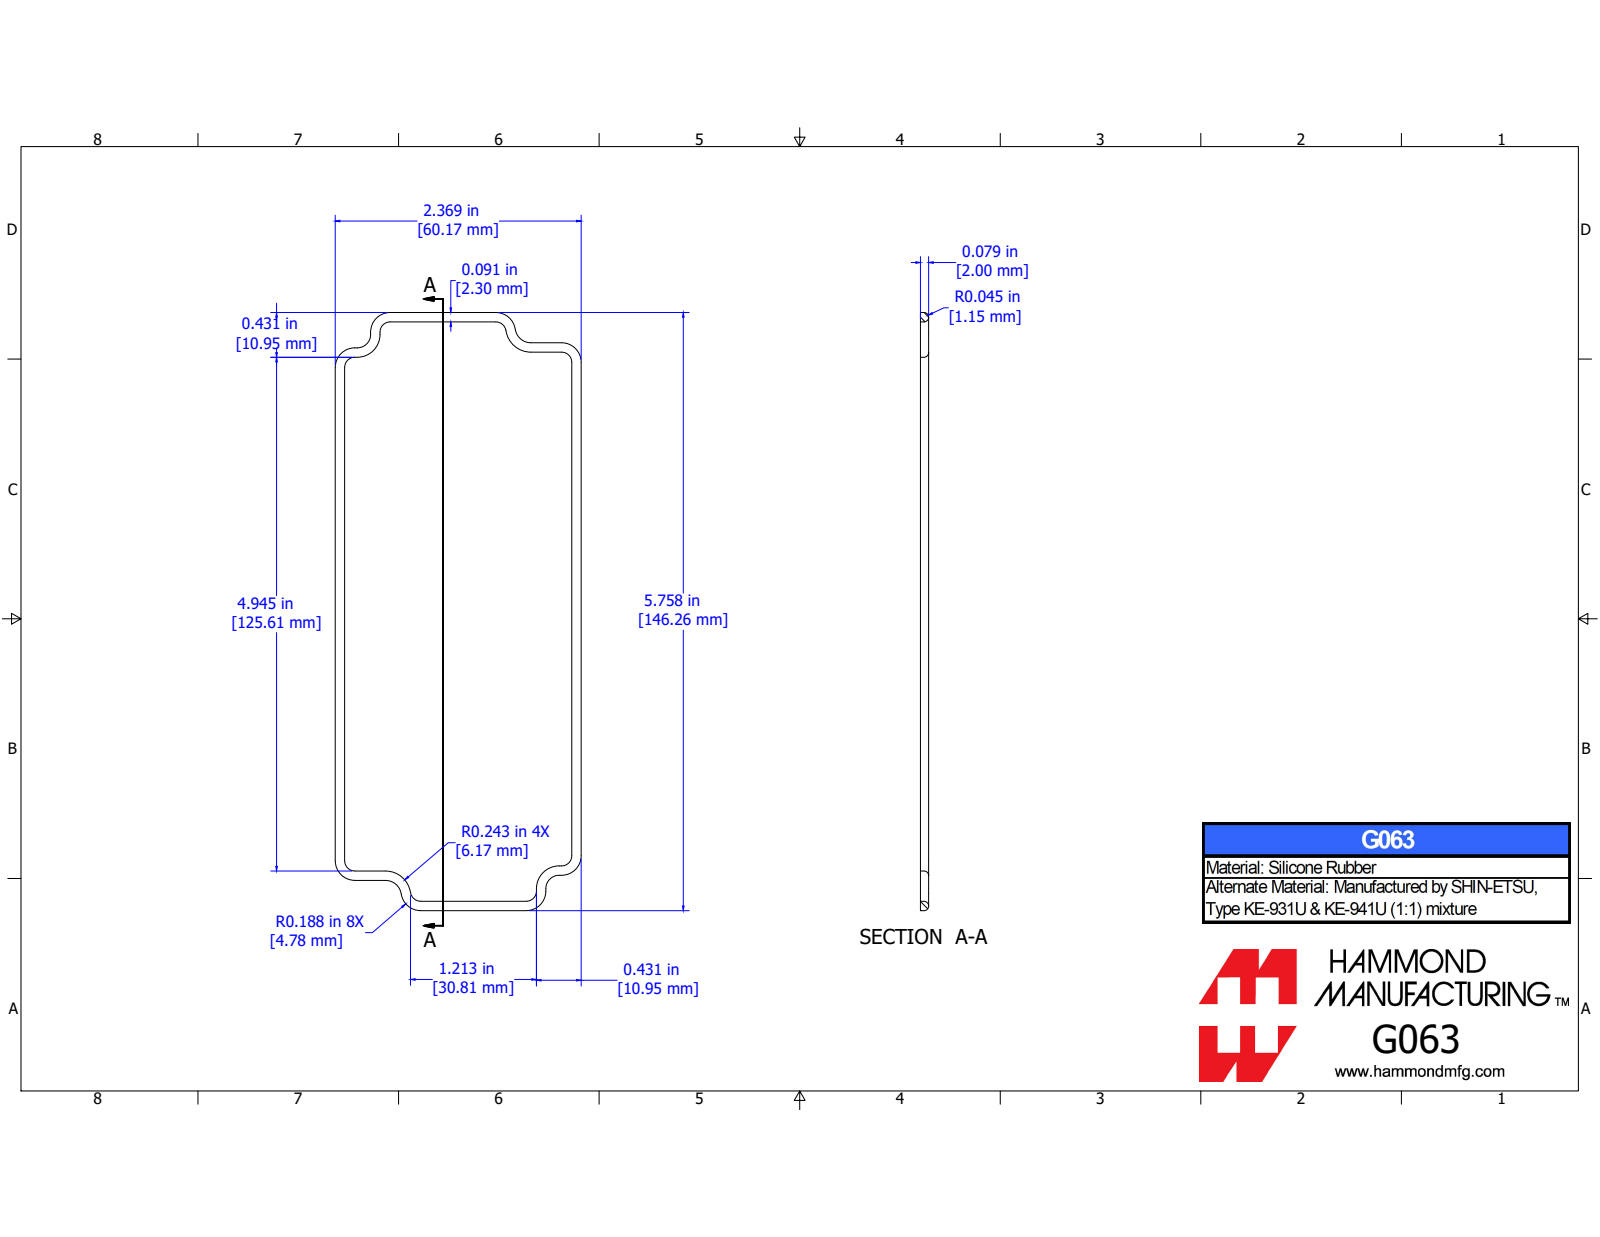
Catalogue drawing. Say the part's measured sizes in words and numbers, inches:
The part is named "1590Z063G". Its 3-D file was written by "SolidWorks 2019 (CONFIG_CONTROL_DESIGN)". It is 1 solid with 154 faces: 40 planar, 24 cylindrical and 90 other. Overall it measures 5.76 by 2.374 by 0.093 inches. Its volume is 0.111 cubic inches and its surface area 4.97 square inches. Partial cylindrical surfaces (rounded edges, fillets, slot ends): 24 of radius 0.039. The main face-to-face distances are 2.27, 5.643, 0.091, 0.331, 5.311, 4.98, 0.093, 0.626, 1.645, 0.322.
